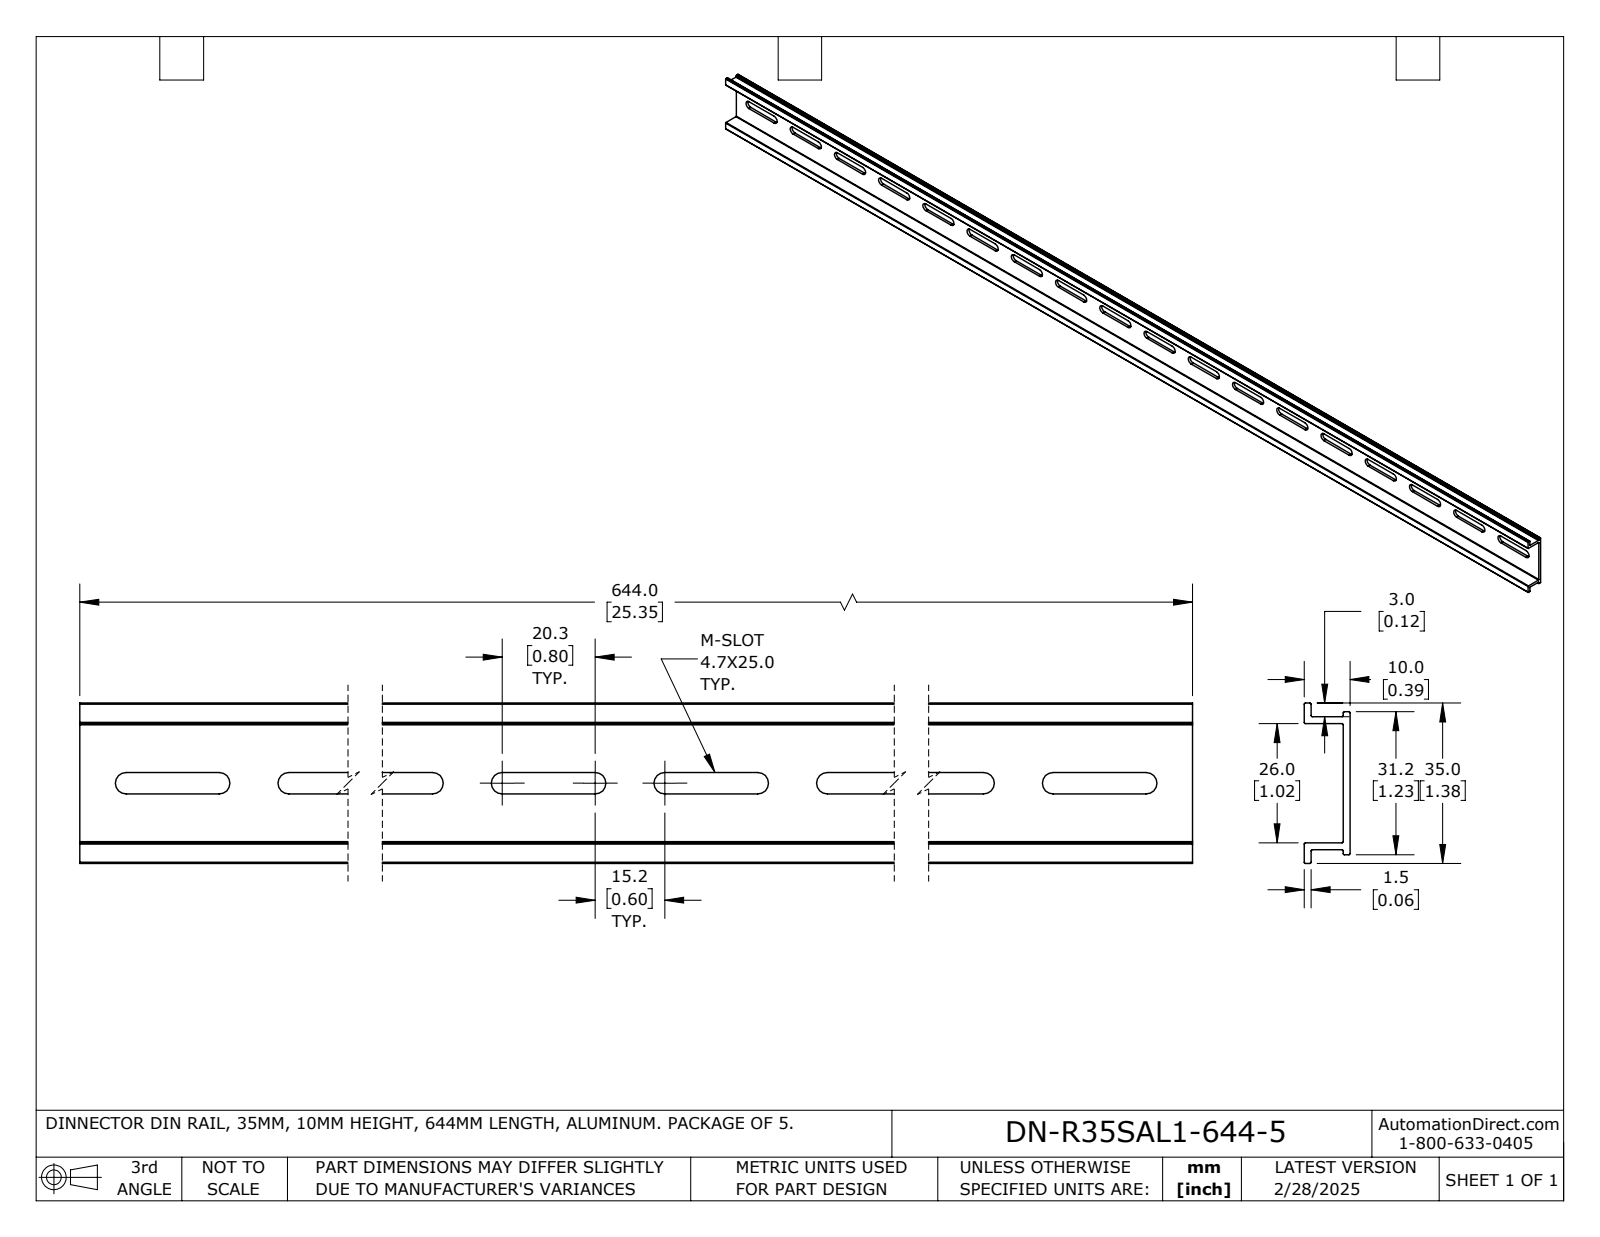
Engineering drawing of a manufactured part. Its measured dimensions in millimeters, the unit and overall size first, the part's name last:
Units: millimetres
Overall size (bounding box): 644 × 35 × 10
Partial cylindrical surfaces — rounded edges, fillets, slot ends (radius × count): R2.35 ×36, R0.27 ×16
Main face-to-face distances: 1.5, 27.5, 8.5, 26, 10, 29, 7, 1.1, 2.6, 28.6
Volume: 49 273 mm³ · Surface area: 68 154 mm²
Bodies: 1 solid, 106 faces (54 planar, 52 cylindrical, 0 other)
Part name (STEP PRODUCT): DN-R35SAL1-644-5_Default
STEP written by: SolidWorks 2024 (CONFIG_CONTROL_DESIGN)
